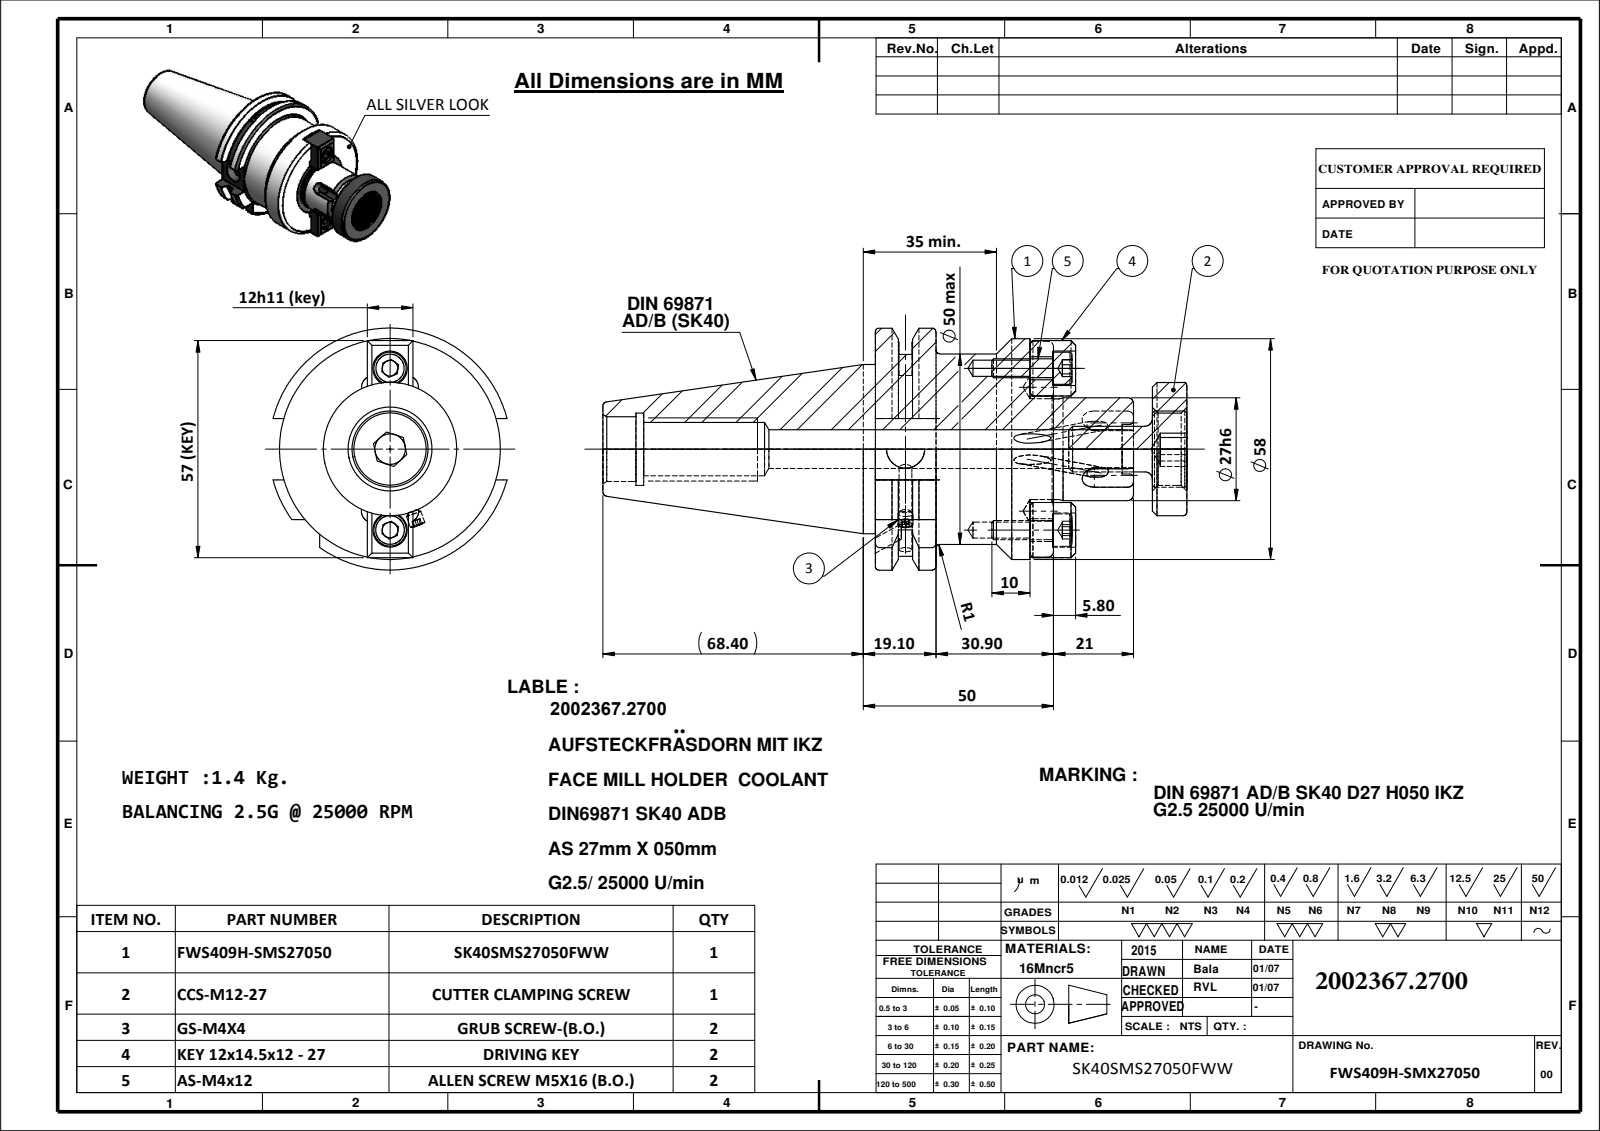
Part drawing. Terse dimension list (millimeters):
name: CCS-M12-27; CCS-M12-27-1; 91406-AS327050; SK40SMS27050FWW R00 (+4 more)
written by: SolidWorks 2009 (CONFIG_CONTROL_DESIGN)
unit: mm
bodies: 9 solids, 353 faces (144 planar, 88 cylindrical, 121 other)
size: 153.4 × 63.55 × 61.48
volume: 189 245 mm³; area: 40 120 mm²
holes: 4× ⌀3, 2× ⌀4.2, 2× ⌀6, 2× ⌀9, 1× ⌀3.3, 1× ⌀10, 1× ⌀10.2, 1× ⌀13, 1× ⌀14, 1× ⌀17, 1× ⌀19
bosses: 2× ⌀8.5, 2× ⌀5, 2× ⌀4, 1× ⌀58, 1× ⌀50, 1× ⌀44.45, 1× ⌀35, 1× ⌀27
rounds: 4× R2, 4× R3, 1× R28.12, 1× R31.77
face distances: 46.8, 81.8, 35, 15.9, 30.9, 65.9, 72.8, 56.9, 26, 9
hole spacings: 21.25, 42.5
